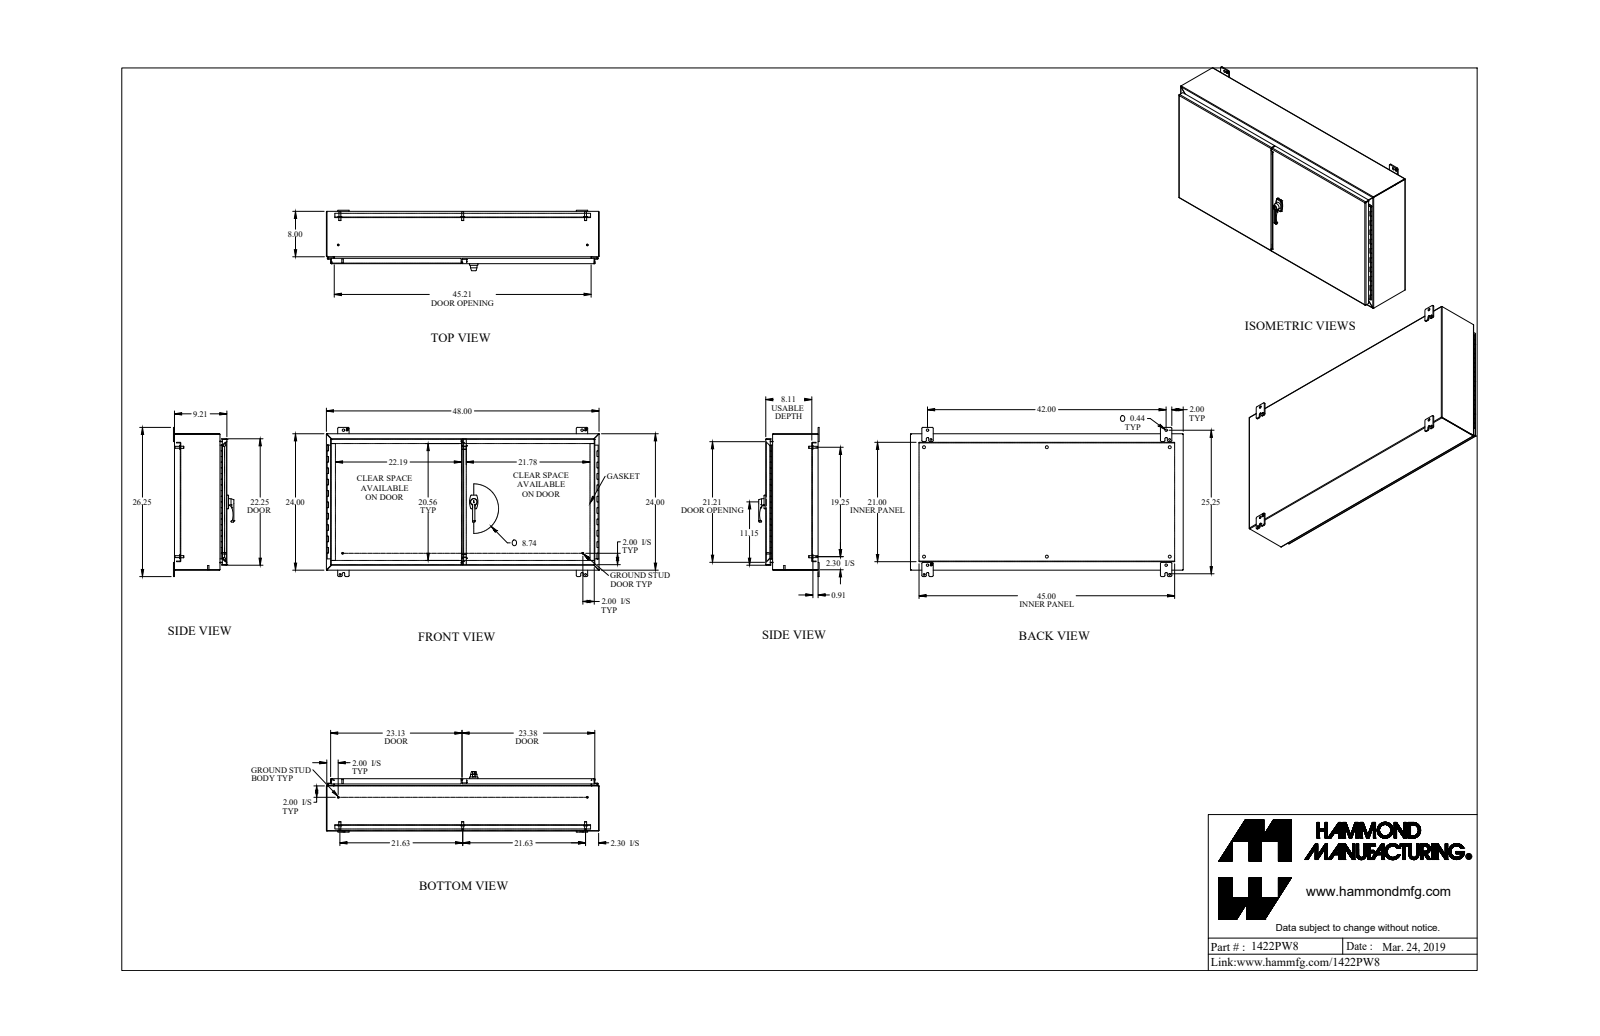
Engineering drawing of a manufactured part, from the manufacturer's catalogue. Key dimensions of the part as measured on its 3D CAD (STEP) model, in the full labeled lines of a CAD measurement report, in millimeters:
Part name (STEP PRODUCT): 1422PW8
STEP written by: SolidWorks 2019 (AUTOMOTIVE_DESIGN)
Units: millimetres
Bodies: 0 solids, 1493 faces (920 planar, 423 cylindrical, 150 other)
Overall size (bounding box): 1219.2 × 666.8 × 270.2
Round holes (diameter × count): ⌀7.7 ×8, ⌀7.8 ×7, ⌀12.7 ×6, ⌀5.5 ×4, ⌀8 ×4, ⌀11.1 ×4, ⌀11.3 ×4, ⌀5.5 ×3, ⌀2.8 ×2, ⌀3.2 ×2, ⌀4 ×2, ⌀4.7 ×2
Round bosses / shafts (diameter × count): ⌀25.4 ×7, ⌀16.5 ×6, ⌀9.5 ×6, ⌀8.4 ×6, ⌀12.7 ×5, ⌀8 ×4, ⌀7.1 ×4, ⌀6.4 ×4
Partial cylindrical surfaces — rounded edges, fillets, slot ends (radius × count): R4.8 ×27, R1.2 ×18, R3.6 ×18, R0.9 ×16, R1.3 ×16, R2.7 ×16, R2.5 ×9, R1.1 ×8
Main face-to-face distances: 1.8, 229.7, 231.5, 2.4, 2.4, 23.8, 232.1, 233.9, 205.9, 203.5
Hole centre spacings: 549.3, 43, 1138.6, 1150.8, 1182.8, 1232.8, 152.4, 589.4
